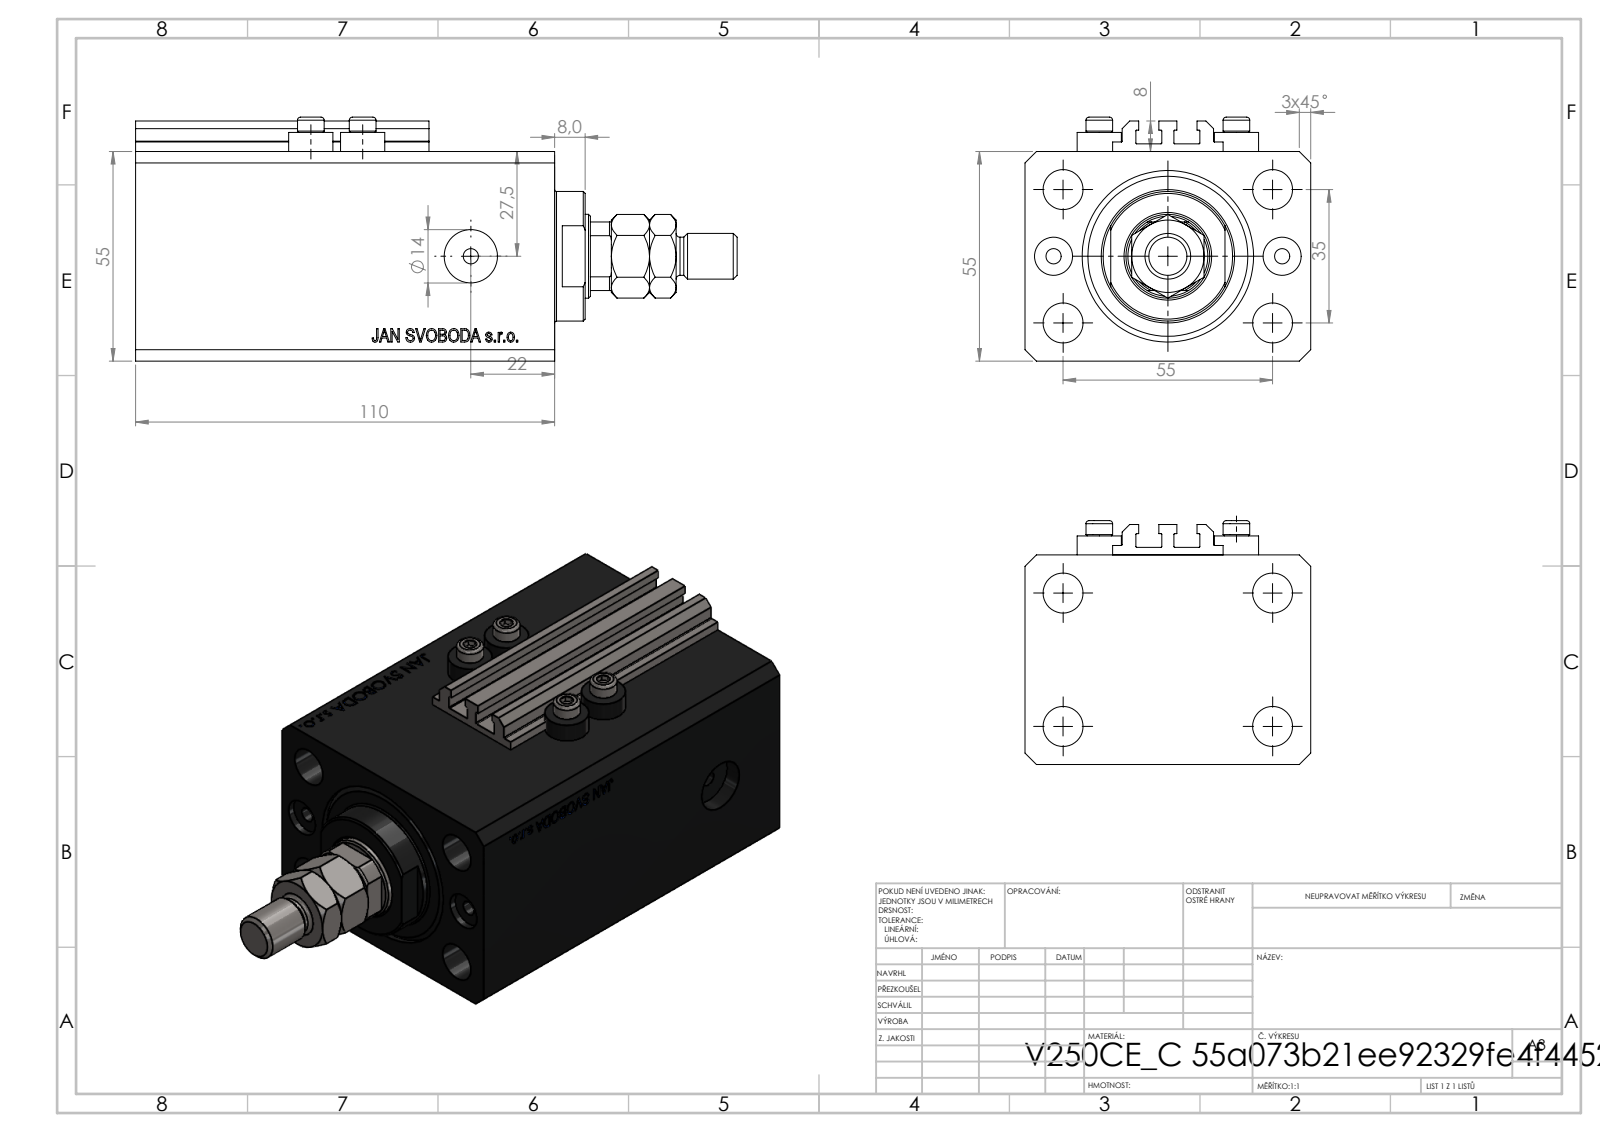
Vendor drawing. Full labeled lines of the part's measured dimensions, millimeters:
Part name (STEP PRODUCT): V250CE_C; V250CE_C_VCP; ALLEN BOLT V250CE; MTA (+1 more)
STEP written by: SolidWorks 2019 (CONFIG_CONTROL_DESIGN)
Units: millimetres
Bodies: 9 solids, 1082 faces (518 planar, 90 cylindrical, 474 other)
Overall size (bounding box): 157.9 × 75 × 64
Volume: 415 843 mm³ · Surface area: 96 090 mm²
Round holes (diameter × count): ⌀4 ×8, ⌀10.5 ×5, ⌀10 ×2, ⌀14 ×2, ⌀22 ×1, ⌀32 ×1, ⌀45 ×1
Round bosses / shafts (diameter × count): ⌀11.6 ×4, ⌀7 ×4, ⌀34 ×1, ⌀12 ×1, ⌀10 ×1
Partial cylindrical surfaces — rounded edges, fillets, slot ends (radius × count): R0.2 ×10, R10.5 ×1
Main face-to-face distances: 55, 75, 110, 82.9, 27.1, 9.9, 73, 100.1, 2.5, 3
Hole centre spacings: 17.68, 32.6, 60.1, 13.6, 30, 35, 36, 38.48
